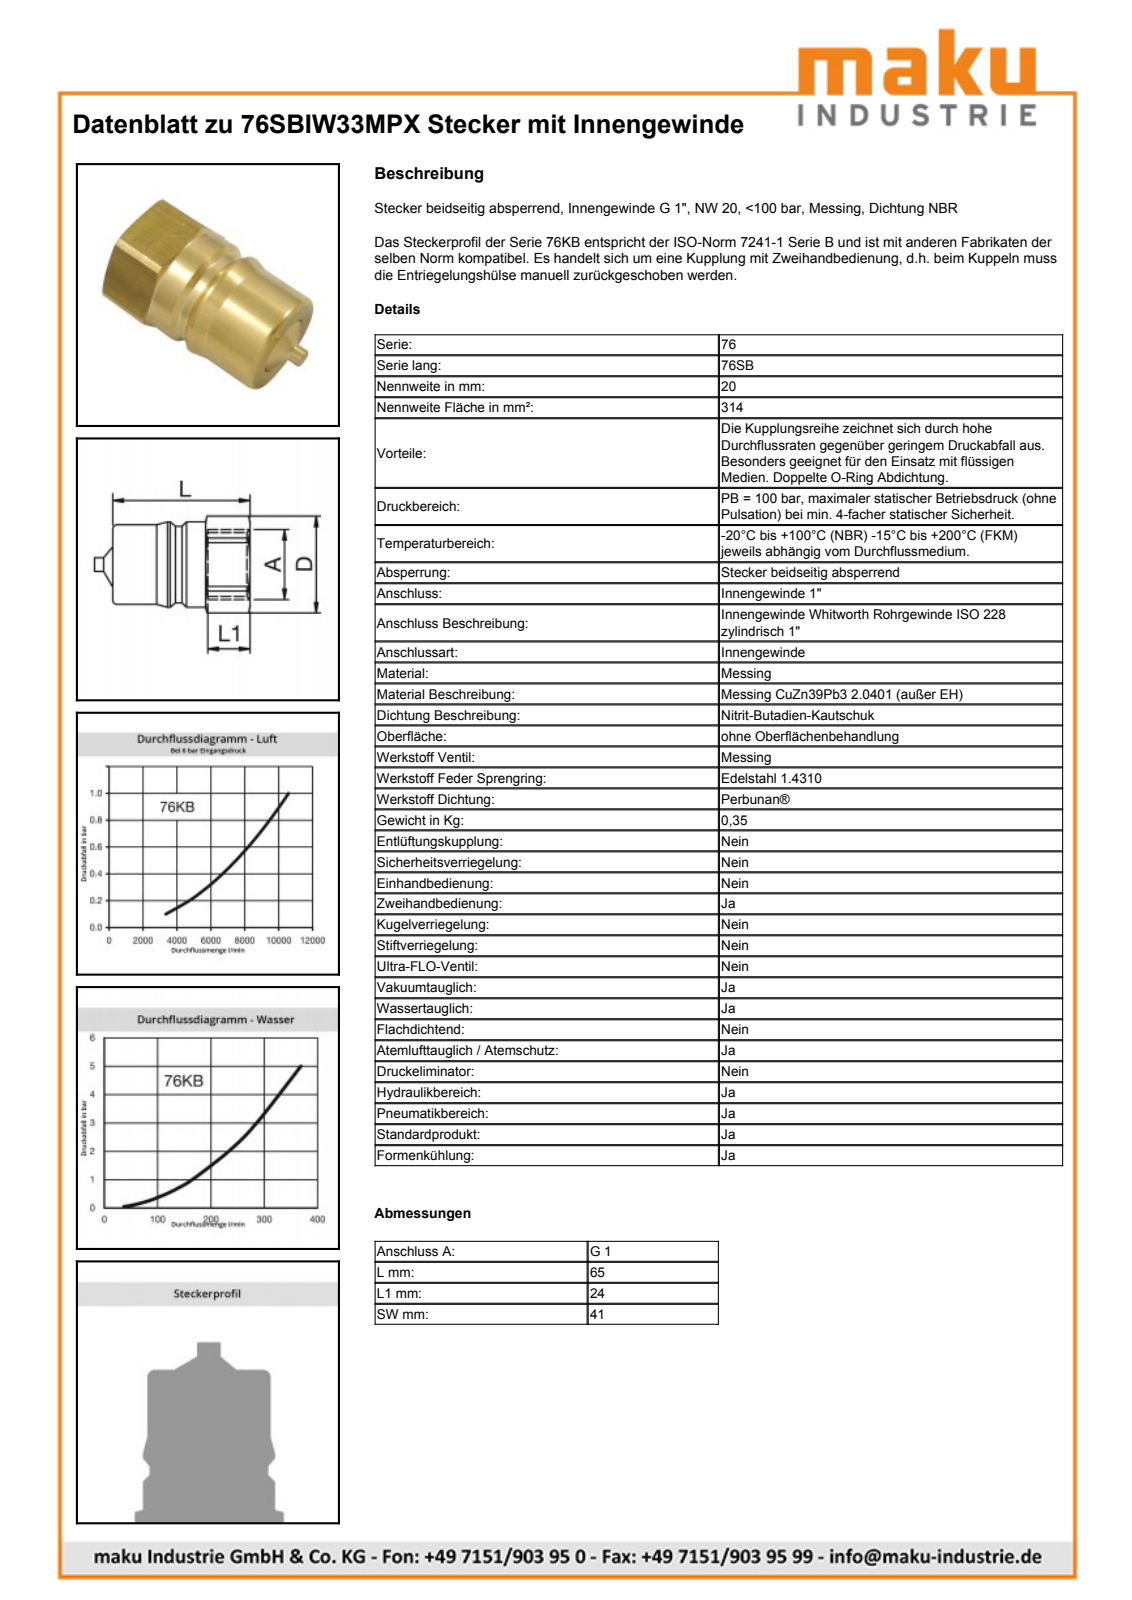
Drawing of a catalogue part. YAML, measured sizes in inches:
part_name: "D107766"
step_written_by: "Autodesk Inventor 2013 (AUTOMOTIVE_DESIGN)"
units: inches
bodies: {solids: 1, faces: 49, planar: 12, cylindrical: 16, other: 21}
overall_size: [2.892, 1.809, 1.614]
volume: 3.956
surface_area: 21.58
round_holes:
  - {diameter: 0.835, count: 1}
  - {diameter: 0.949, count: 1}
  - {diameter: 1.193, count: 1}
round_bosses_or_shafts:
  - {diameter: 1.594, count: 1}
  - {diameter: 1.486, count: 1}
  - {diameter: 1.429, count: 1}
  - {diameter: 0.945, count: 1}
  - {diameter: 0.823, count: 1}
  - {diameter: 0.256, count: 1}
partial_cylinders:
  - {radius: 0.905, count: 1}
face_to_face_distances: [1.614, 1.615, 2.559, 0.944, 0.333, 1.948, 2.892, 2.065, 1.732, 0.118]
